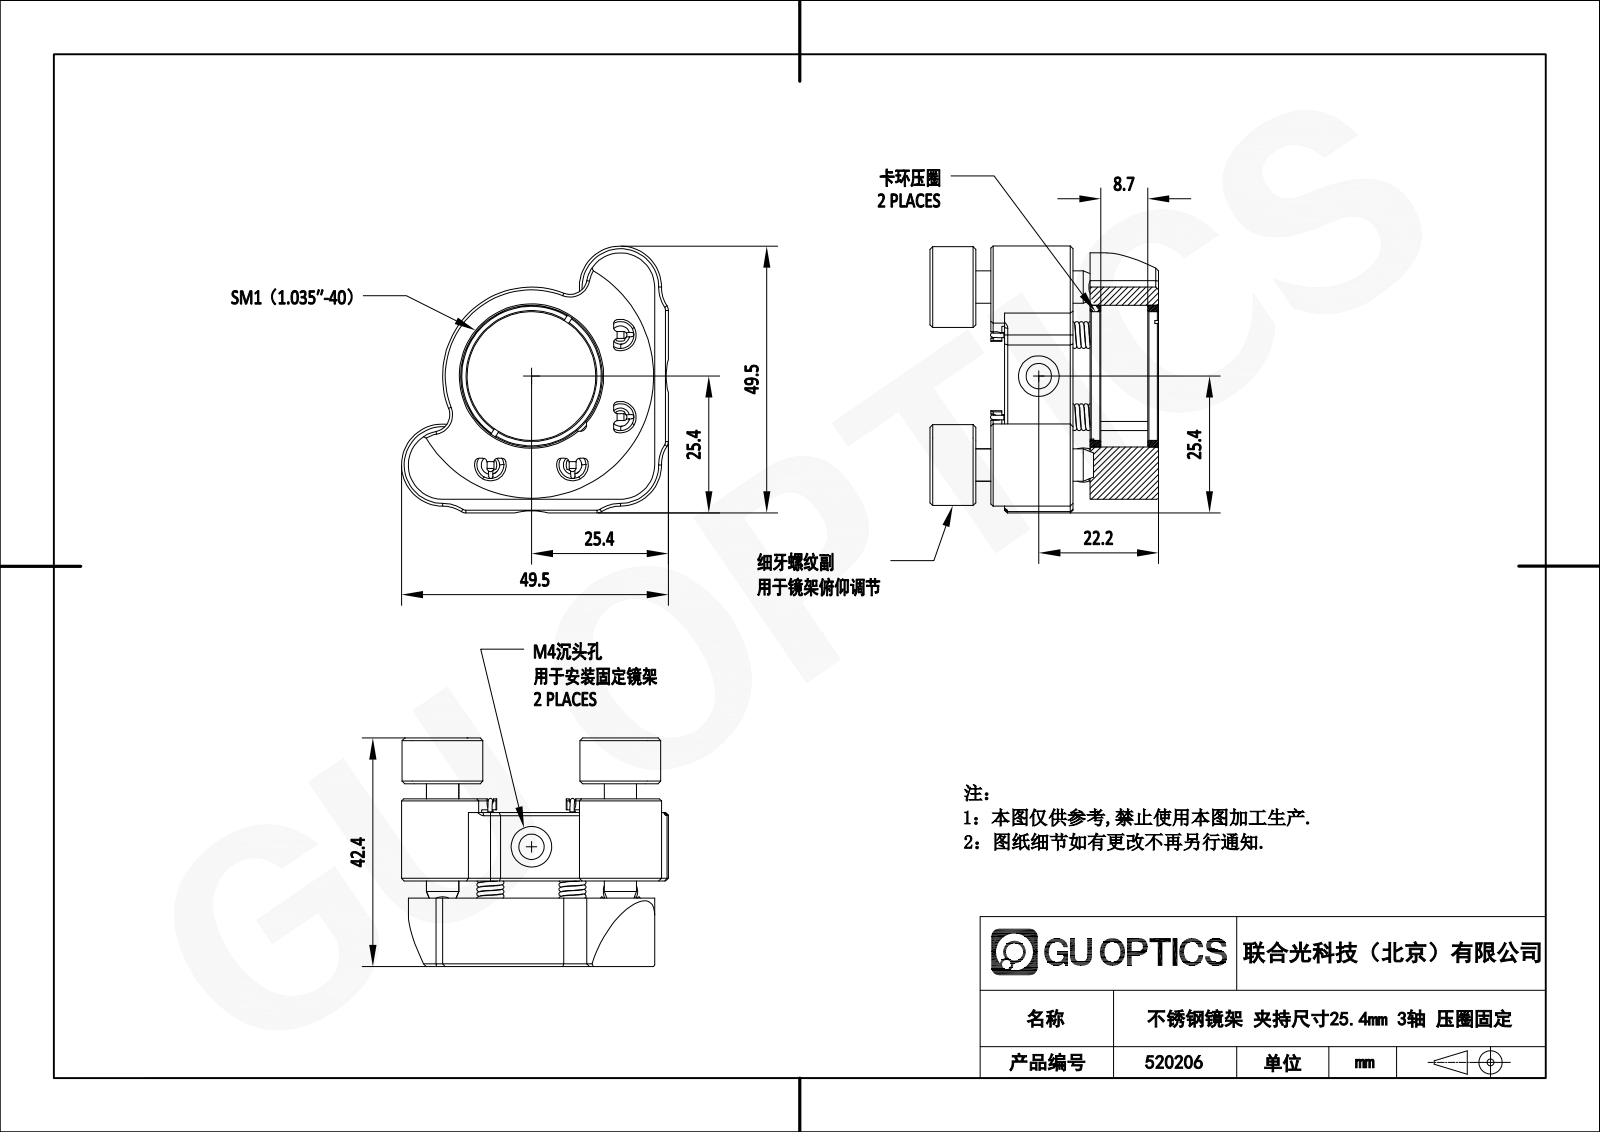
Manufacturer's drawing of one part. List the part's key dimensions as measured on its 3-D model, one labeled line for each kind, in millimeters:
Part name (STEP PRODUCT): 替代进口不锈钢光学调整架前面板，卡圈固定式_1.1.20.13.1_ZJO-SM1.0; ZFK不锈钢透镜卡环压圈_1.8.9.2_ZFKS-K1.0; DXS-0625标准型六角调节器 _3.2.2.16.1-DXS-0625-26.6; DXG，平面螺纹旋钮_3.2.10.19-DXG-M0625-15-8.5S (+2 more)
STEP written by: SolidWorks 2021 (CONFIG_CONTROL_DESIGN)
Units: millimetres
Bodies: 23 solids, 634 faces (204 planar, 175 cylindrical, 255 other)
Overall size (bounding box): 49.53 × 49.53 × 42.7
Volume: 28 531 mm³ · Surface area: 20 489 mm²
Round holes (diameter × count): ⌀6.35 ×7, ⌀3.99 ×3, ⌀4 ×3, ⌀6 ×3, ⌀7 ×3, ⌀2.01 ×2, ⌀4.7 ×2, ⌀7.54 ×2, ⌀23.89 ×1
Round bosses / shafts (diameter × count): ⌀4 ×6, ⌀15 ×3, ⌀15.24 ×2, ⌀26.29 ×1
Partial cylindrical surfaces — rounded edges, fillets, slot ends (radius × count): R0.79 ×16, R6.48 ×14, R0.64 ×8, R1 ×4, R1.93 ×4, R2.92 ×4, R6.35 ×3, R1.59 ×2
Main face-to-face distances: 12.7, 15.87, 2.54, 3.17, 15.24, 31.11, 18.41, 28.57, 8.5, 13.84
Hole centre spacings: 8.89, 18.18, 24.13, 23.35, 5, 15.24, 25.72, 33.02
